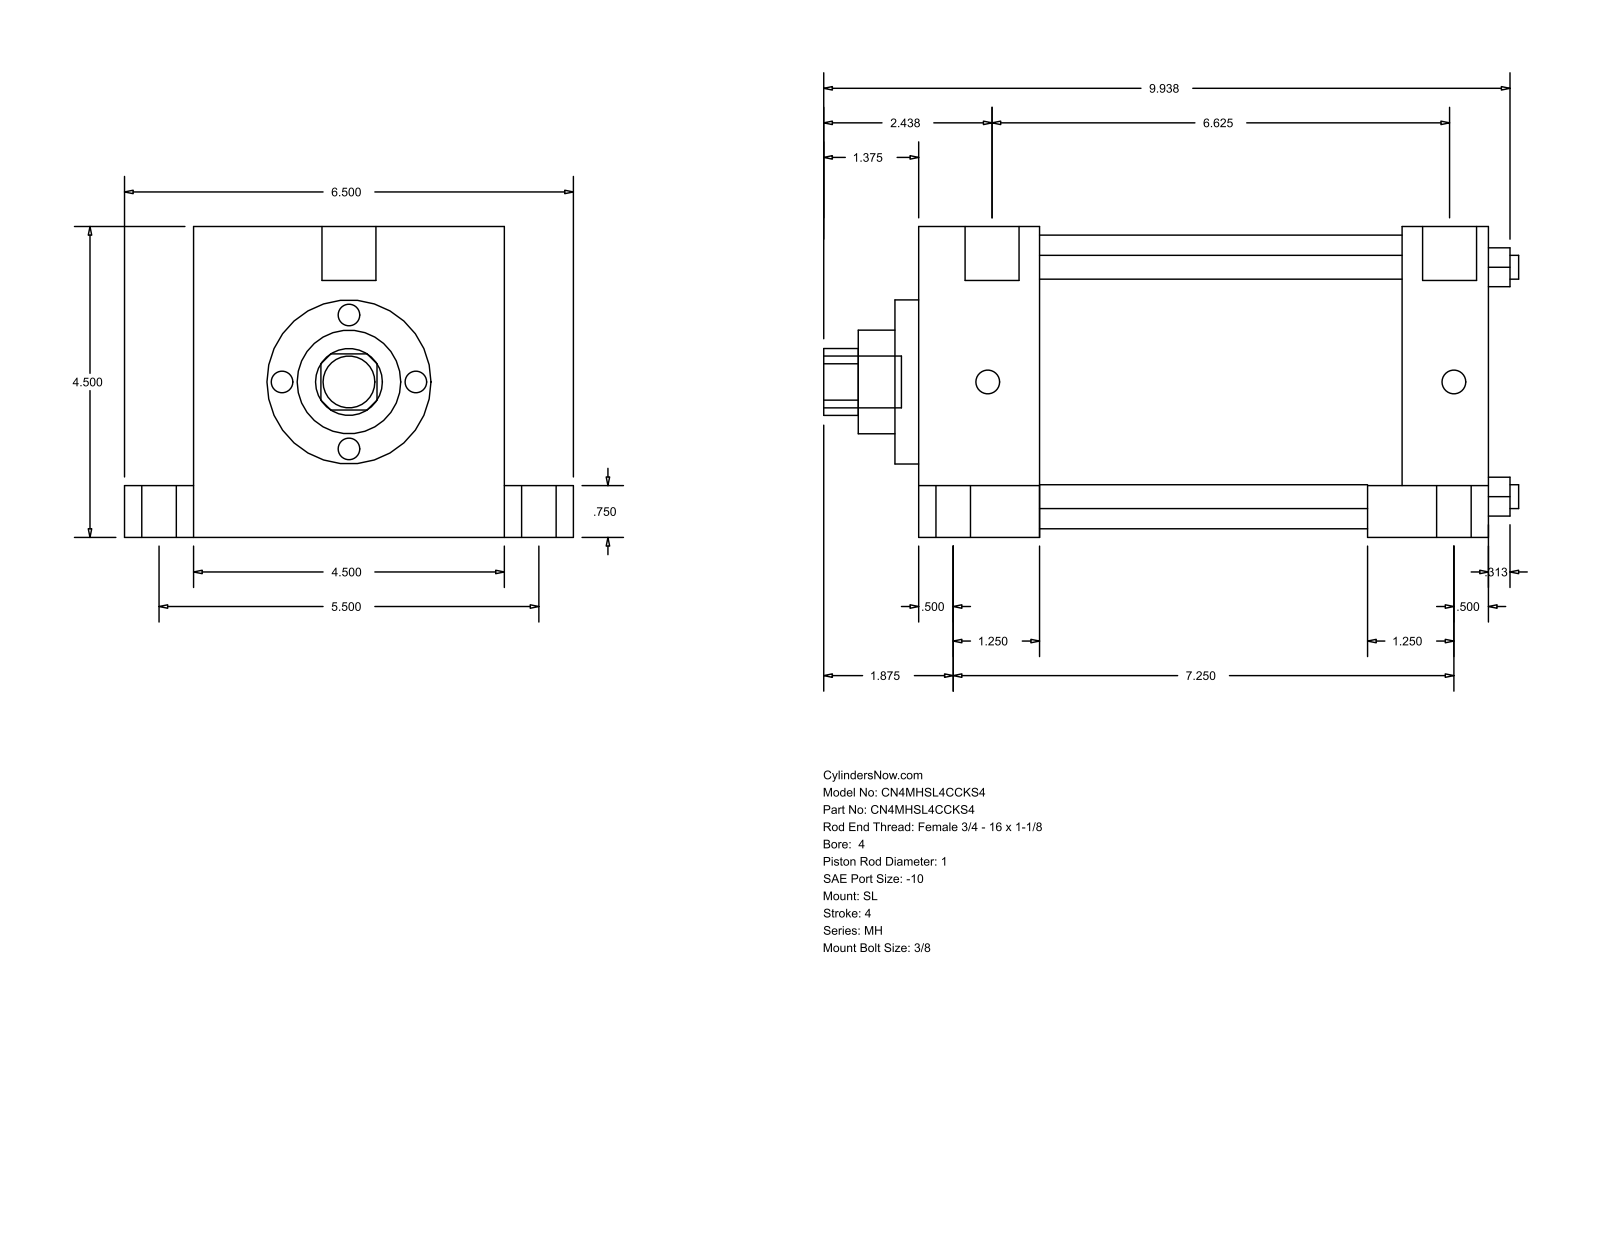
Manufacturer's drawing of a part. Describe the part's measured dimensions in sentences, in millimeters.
The part is named "MH_SL__0400_1". Its 3-D file was written by "GSSL Pune (CONFIG_CONTROL_DESIGN)". It is 0 solids with 110 faces: 77 planar, 33 cylindrical and 0 other. Overall it measures 255.59 by 165.1 by 114.3 millimeters. Round holes: 4 of diameter 8.76, 1 of diameter 25.4, 1 of diameter 38.1, 1 of diameter 60.33, 1 of diameter 107.95. Round bosses or shafts: 5 of diameter 19.05, 4 of diameter 12.7, 4 of diameter 8.73, 2 of diameter 19.84. Partial cylindrical surfaces (rounded edges, fillets, slot ends): 1 of radius 12.29. The main face-to-face distances are 114.3, 209.55, 44.46, 165.09, 177.8, 133.34, 31.75, 25.4, 139.7, 19.05. The hole center spacings are 59.62, 84.32, 119.25.
